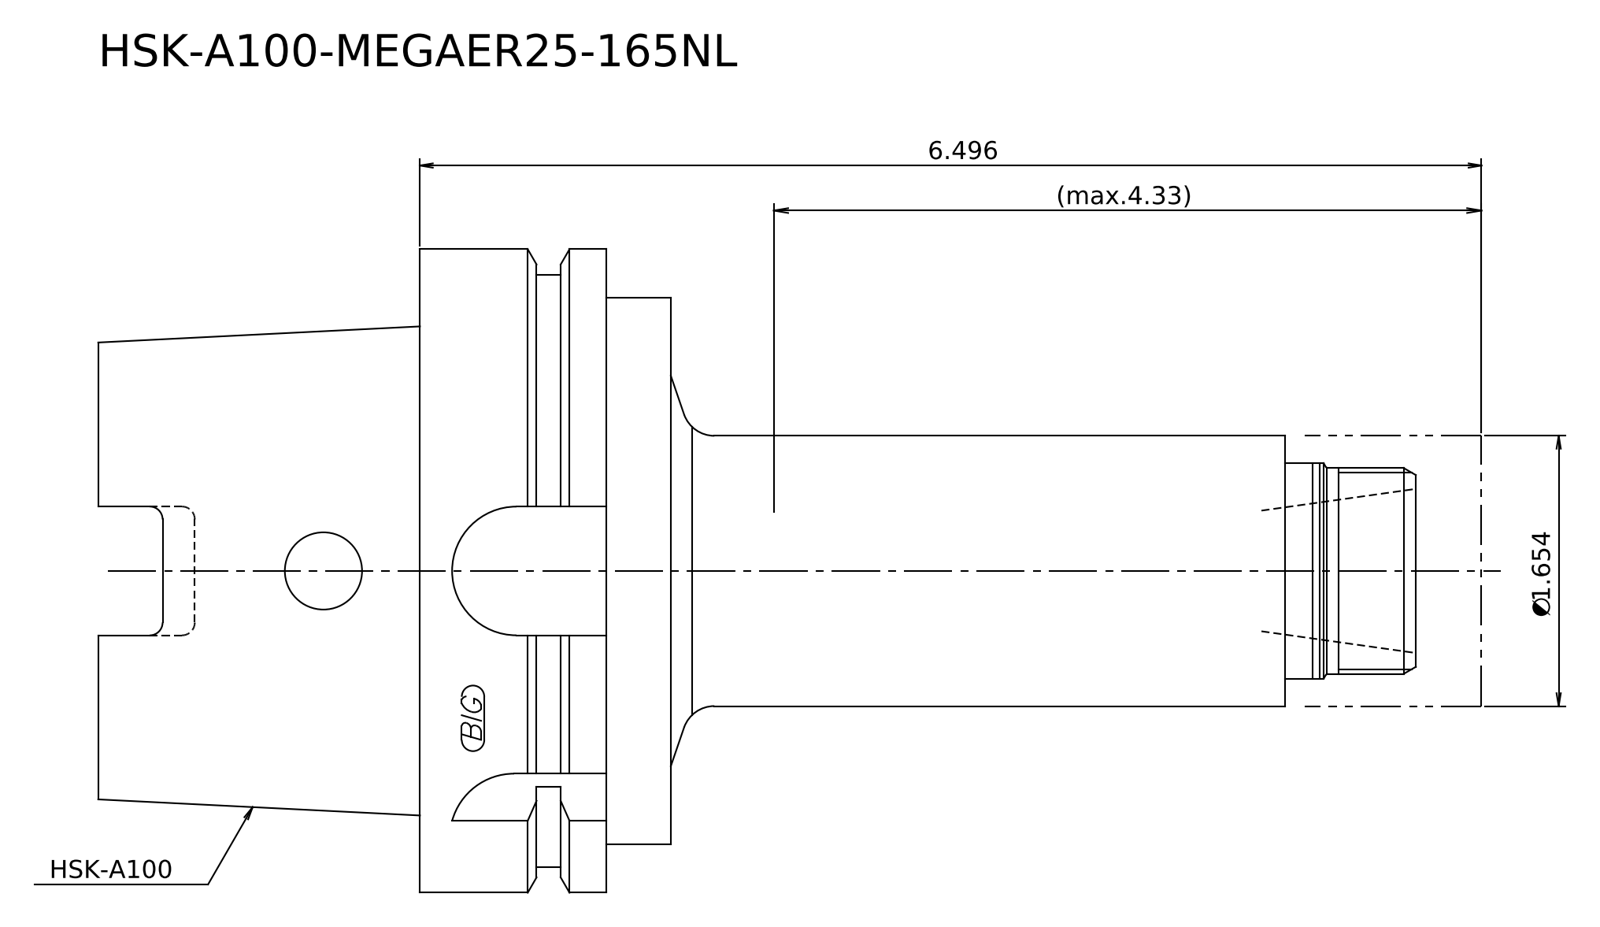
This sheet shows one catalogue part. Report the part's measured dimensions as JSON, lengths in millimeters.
{"step_written_by": "Kubotek KeyCreator 2011 V10.0.2 (22737) (automotive_design)", "units": "millimeters", "bodies": {"solids": 2, "faces": 24, "planar": 10, "cylindrical": 8, "other": 6}, "overall_size": [215, 100, 100], "volume_mm3": 683098, "surface_area_mm2": 60558, "round_bosses_or_shafts": [[100, 1], [92, 1], [85, 1], [42, 1], [33.5, 1], [32, 1]], "face_to_face_distances": [50, 39, 89, 10, 29, 79, 98.5, 108.5, 137.5, 187.5]}
